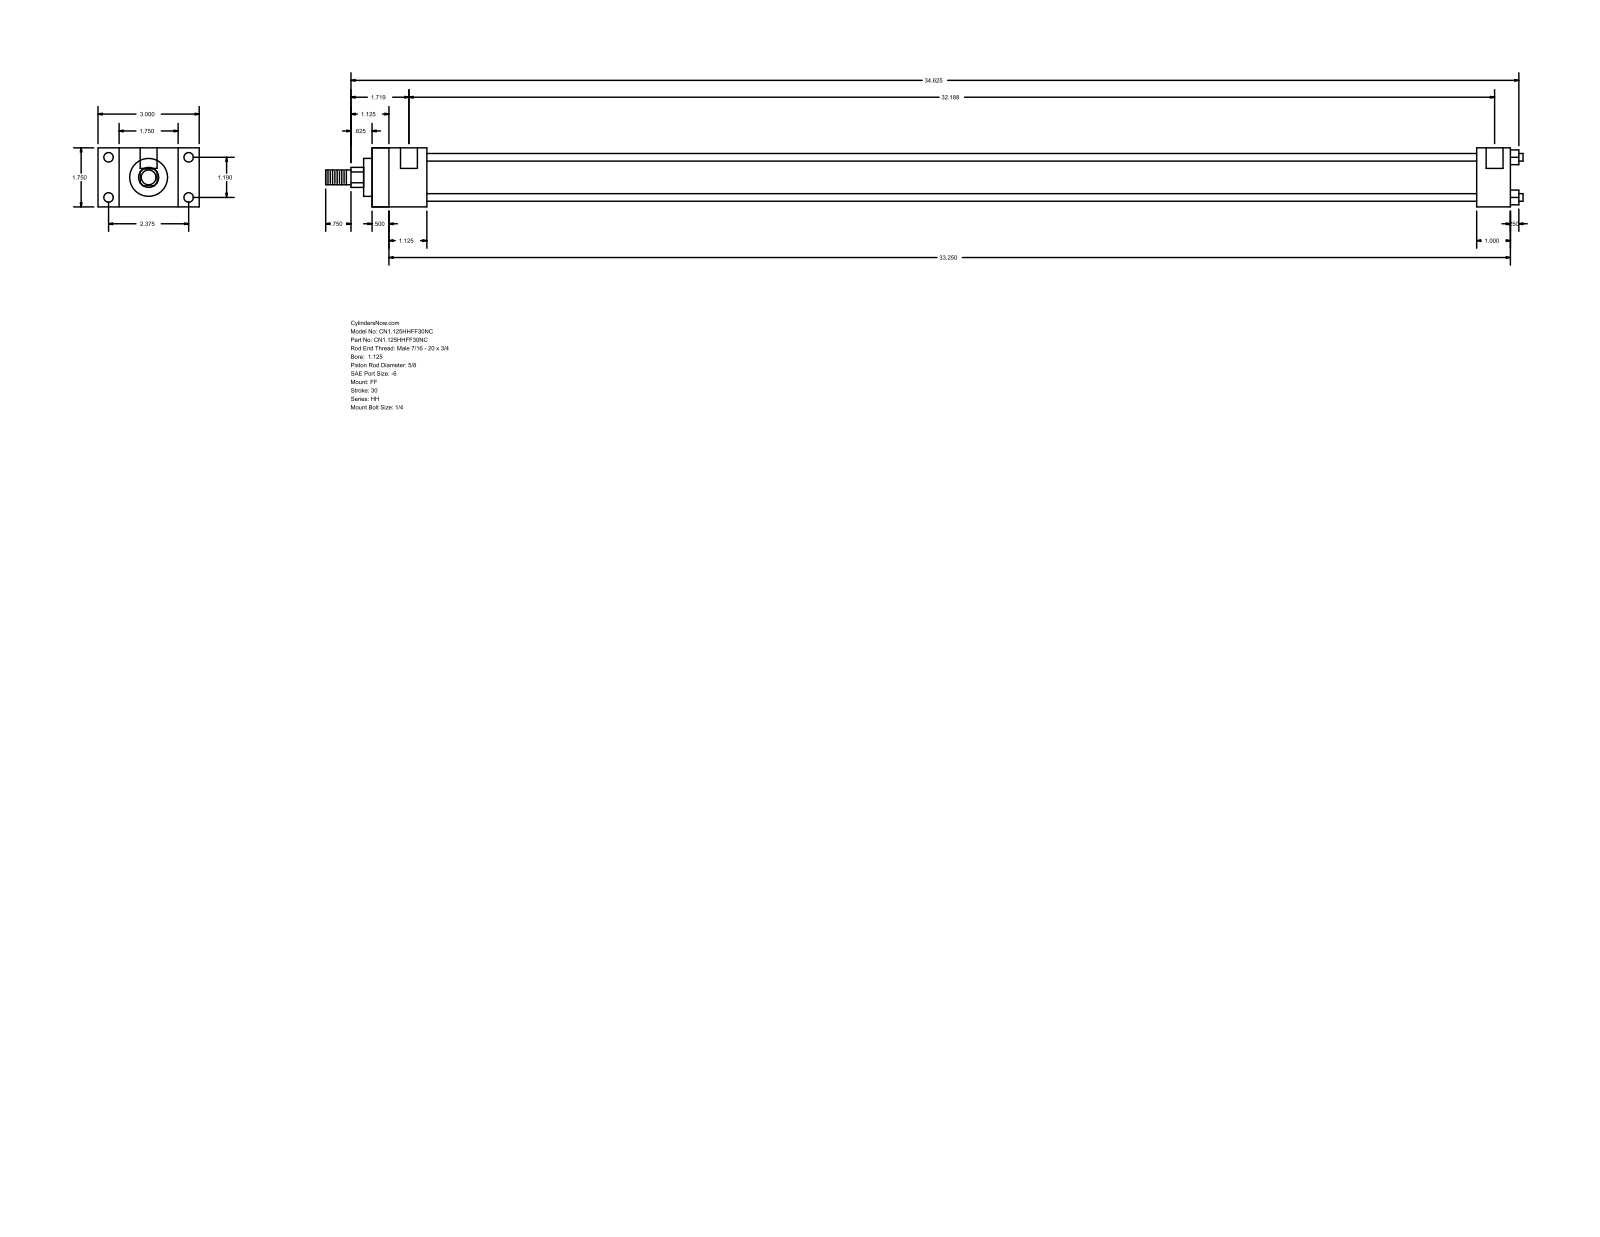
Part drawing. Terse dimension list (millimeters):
name: HH_FF__0112_0.625
written by: GSSL Pune (CONFIG_CONTROL_DESIGN)
unit: mm
bodies: 0 solids, 92 faces (64 planar, 28 cylindrical, 0 other)
size: 901.7 × 76.2 × 44.45
holes: 4× ⌀5.56, 4× ⌀7.14, 2× ⌀12.7
bosses: 4× ⌀5.71, 1× ⌀34.92, 1× ⌀28.57, 1× ⌀15.88, 1× ⌀11.11
rounds: 1× R7.54
face distances: 44.46, 857.24, 15.87, 12.69, 844.55, 28.58, 60.33, 41.27, 831.85, 819.16
hole spacings: 30.22, 60.32, 67.47, 814.39, 3.17, 817.56
